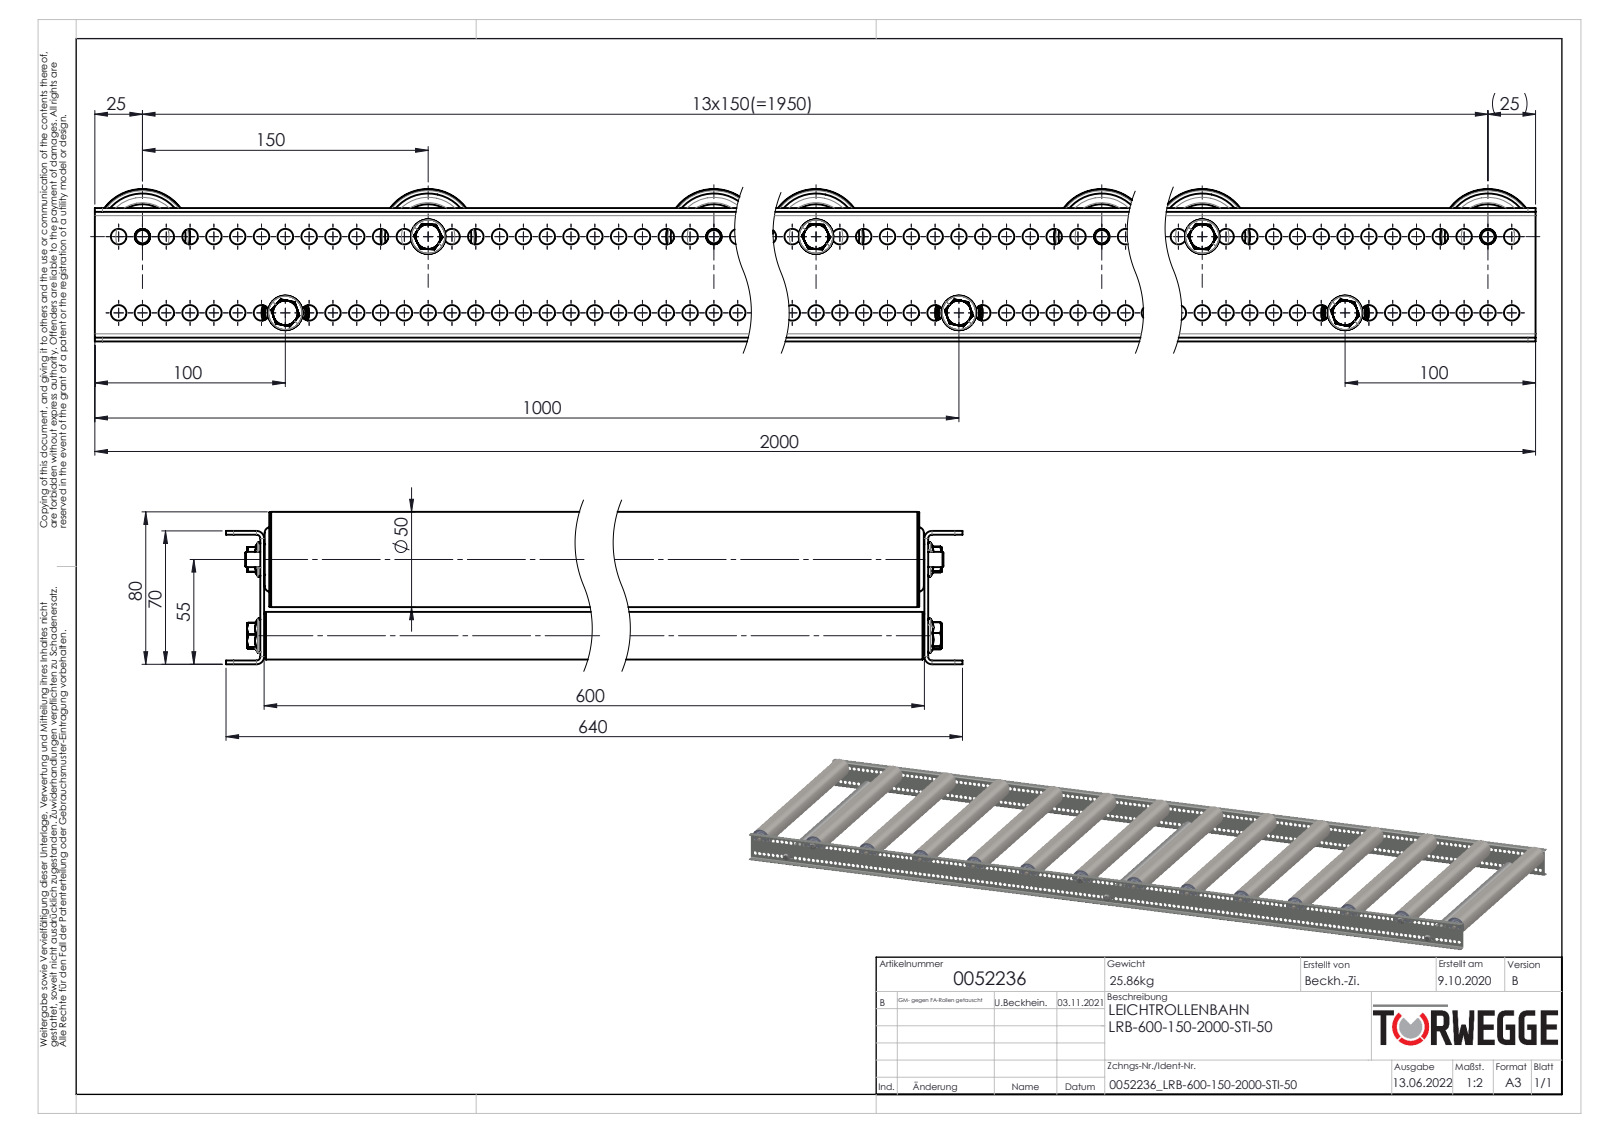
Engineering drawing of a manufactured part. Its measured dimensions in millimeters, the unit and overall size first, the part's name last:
Units: millimetres
Overall size (bounding box): 2000 × 640 × 80
Round holes (diameter × count): ⌀8.2 ×318, ⌀17.1 ×14, ⌀18.5 ×14, ⌀27.7 ×14, ⌀45.3 ×14, ⌀47 ×14, ⌀7.6 ×11, ⌀6.8 ×6, ⌀12 ×3, ⌀12.2 ×3, ⌀19.2 ×3, ⌀21 ×3
Round bosses / shafts (diameter × count): ⌀8 ×17, ⌀50 ×14, ⌀49.5 ×14, ⌀47.3 ×14, ⌀29.7 ×14, ⌀27.4 ×14, ⌀27.3 ×14, ⌀16 ×14
Partial cylindrical surfaces — rounded edges, fillets, slot ends (radius × count): R0.6 ×22, R0.75 ×22, R2.45 ×22, R2.5 ×12, R4.87 ×11, R7 ×11, R4 ×8, R2 ×4
Main face-to-face distances: 2, 602, 68, 600, 604, 70, 66, 18, 20, 620
Hole centre spacings: 12.5, 25, 37.5, 50, 62.5, 75, 87.5, 100
Volume: 3 760 000 mm³ · Surface area: 4 274 000 mm²
Bodies: 350 solids, 6934 faces (1320 planar, 2752 cylindrical, 2862 other)
Part name (STEP PRODUCT): Traversen_KFG_L600; Sicherungsring_DIN471_8x0.8_Circlip DIN 471 - 8 x 0.8; 0026295_Typ-TRG_50x1,5-8; 0039771_Tragrollenrohr-Ø50x1,5STI_KFG_EL600 (+8 more)
STEP written by: SolidWorks 2020 (AUTOMOTIVE_DESIGN)
